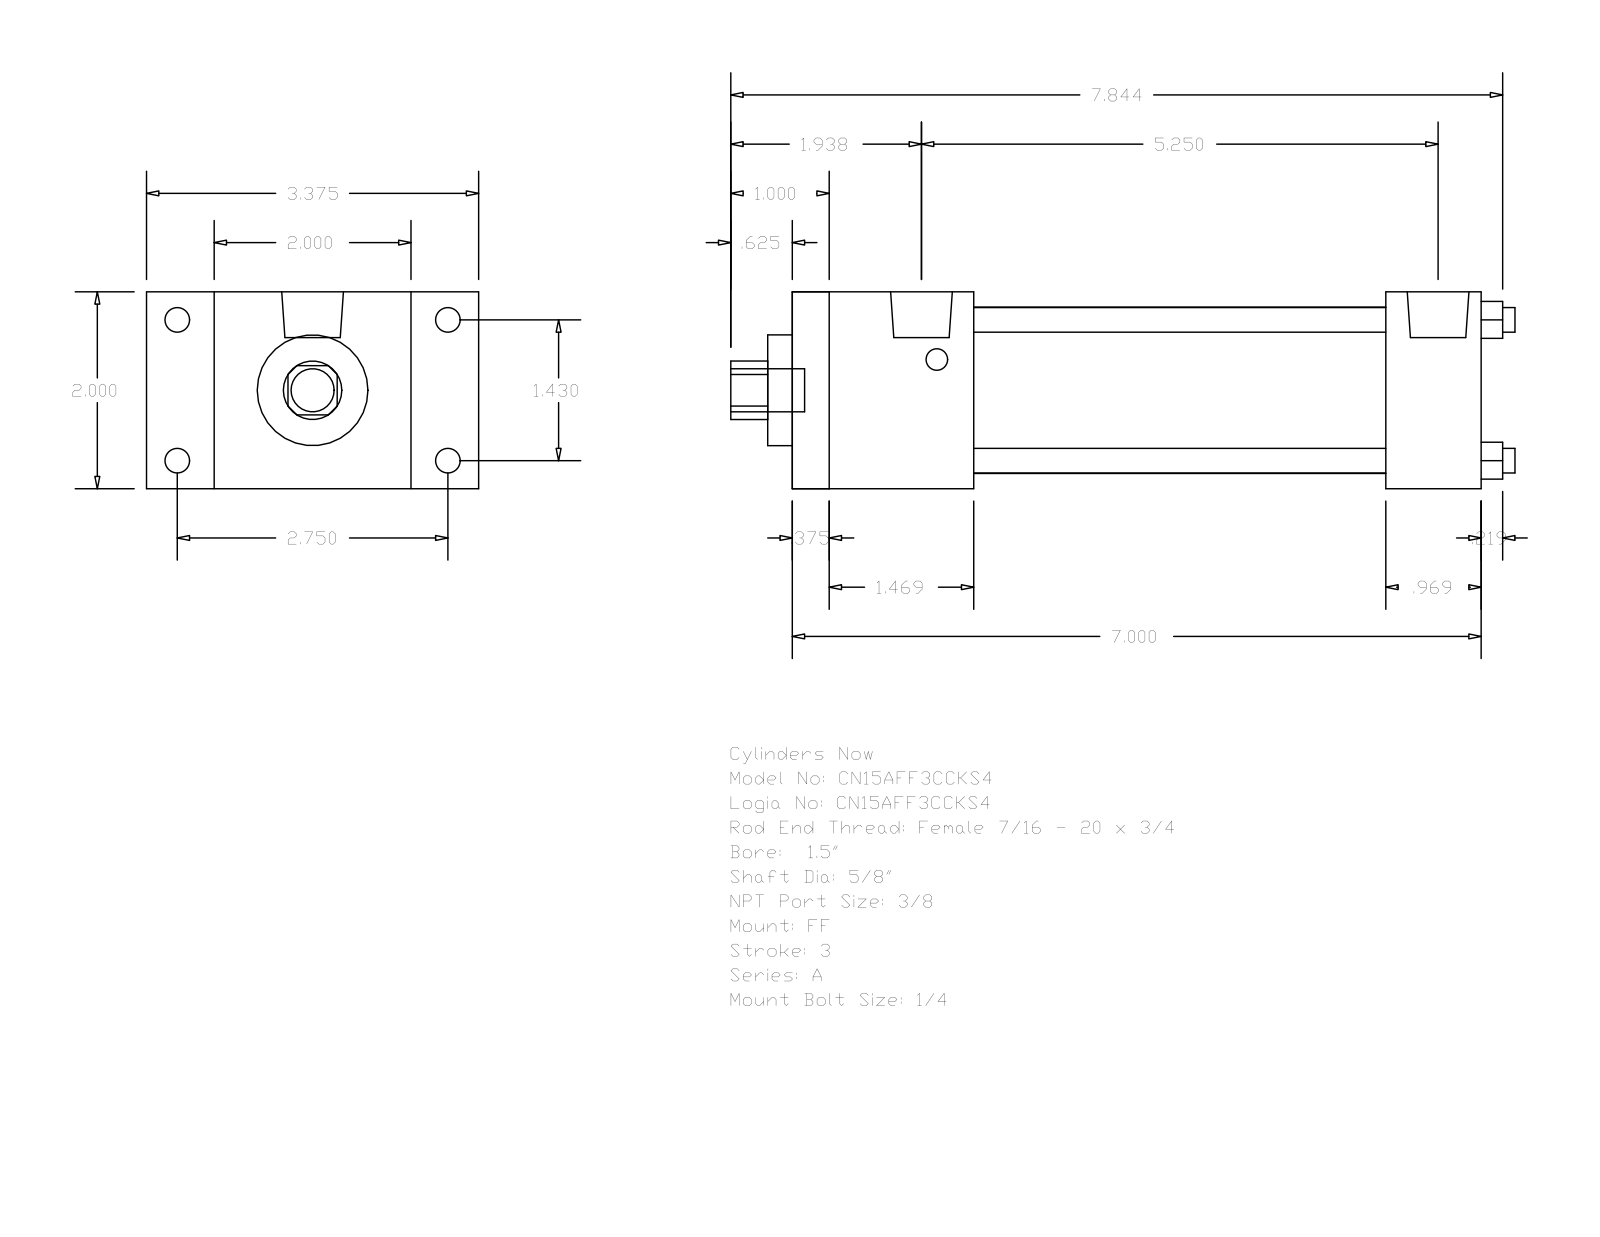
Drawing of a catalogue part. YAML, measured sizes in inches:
part_name: "A_FF__0150_0.625"
step_written_by: "GSSL Pune (CONFIG_CONTROL_DESIGN)"
units: inches
bodies: {solids: 0, faces: 92, planar: 64, cylindrical: 28, other: 0}
overall_size: [7.969, 3.375, 2]
round_holes:
  - {diameter: 0.25, count: 4}
  - {diameter: 0.625, count: 1}
  - {diameter: 1.125, count: 1}
  - {diameter: 1.69, count: 1}
round_bosses_or_shafts:
  - {diameter: 0.25, count: 4}
  - {diameter: 0.219, count: 4}
  - {diameter: 0.627, count: 2}
  - {diameter: 0.437, count: 1}
partial_cylinders:
  - {radius: 0.297, count: 1}
face_to_face_distances: [2, 7, 0.375, 6.625, 1.844, 6.031, 1.469, 5.656, 4.187, 5.156]
hole_center_spacings: [1.011, 1.43, 2.022]
